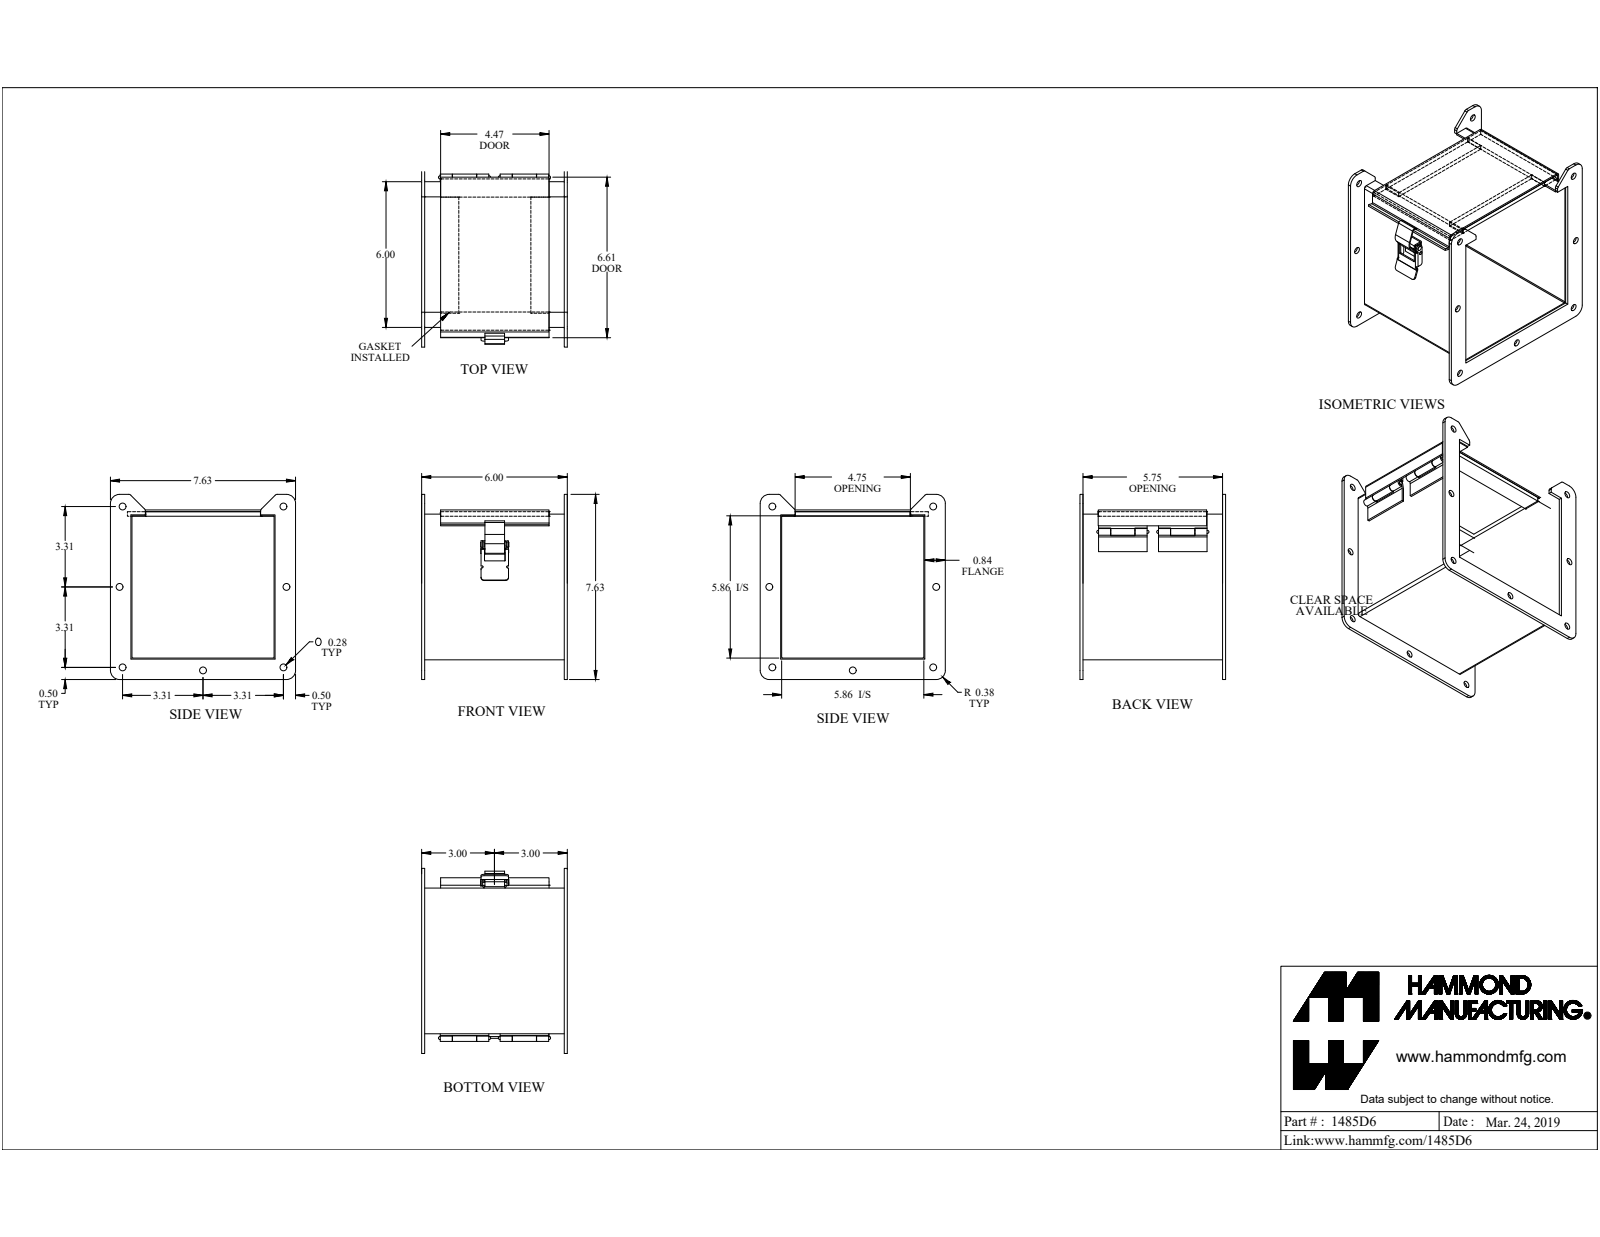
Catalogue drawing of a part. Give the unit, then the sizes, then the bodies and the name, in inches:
Units: inches
Overall size (bounding box): 7.625 × 7.625 × 6
Round holes (diameter × count): ⌀0.281 ×7, ⌀0.125 ×1, ⌀0.13 ×1, ⌀0.164 ×1
Round bosses / shafts (diameter × count): ⌀0.187 ×2, ⌀0.275 ×1, ⌀0.156 ×1, ⌀0.125 ×1, ⌀0.125 ×1
Partial cylindrical surfaces — rounded edges, fillets, slot ends (radius × count): R0.016 ×7, R0.036 ×7, R0.108 ×7, R0.125 ×7, R0.375 ×4, R0.035 ×3, R0.039 ×3, R0.076 ×3
Main face-to-face distances: 0.072, 5.928, 6.1, 6, 5.856, 0.125, 5.875, 6.028, 6.172, 5.75
Hole centre spacings: 7.519, 6.625, 3.315, 3.315, 9.369, 0.285, 1.054, 1.493
Volume: 18.24 in³ · Surface area: 440.8 in²
Bodies: 17 solids, 302 faces (188 planar, 110 cylindrical, 4 other)
Part name (STEP PRODUCT): 1485D6
STEP written by: SolidWorks 2019 (CONFIG_CONTROL_DESIGN)
